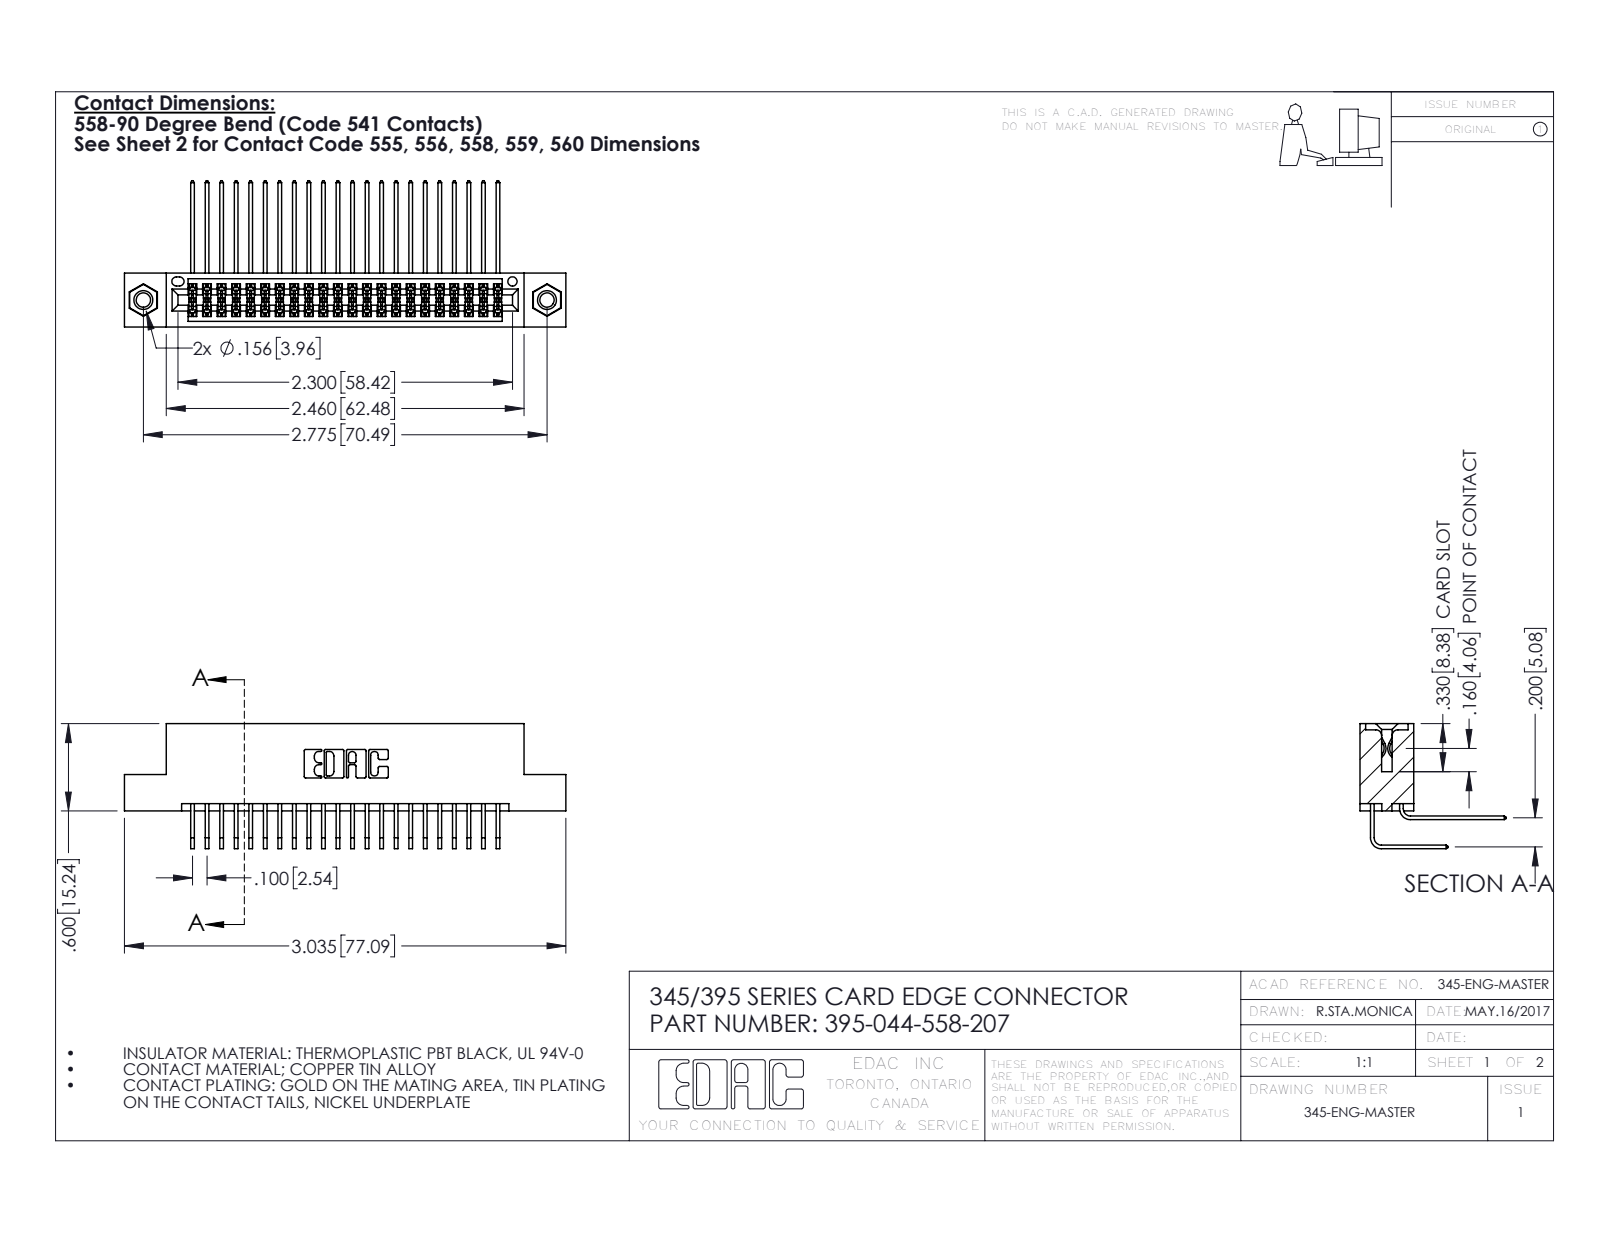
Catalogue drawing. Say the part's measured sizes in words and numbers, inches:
The part is named "345 Part_Flush Mounting Lugs - 0.156 Dia-TI; 345-250-001_345-250-005-103; 345-292-001_558 Tail - 2; 345-292-001_558 559 Tail - 1 (+1 more)". Its 3-D file was written by "SolidWorks 2016 (CONFIG_CONTROL_DESIGN)". It is 47 solids with 2474 faces: 1652 planar, 806 cylindrical and 16 other. Overall it measures 3.035 by 1.005 by 0.859 inches. Its volume is 0.46 cubic inches and its surface area 18.58 square inches. Round holes: 2 of diameter 0.098, 2 of diameter 0.125, 2 of diameter 0.156, 1 of diameter 0.064. Round bosses or shafts: 2 of diameter 0.155. Partial cylindrical surfaces (rounded edges, fillets, slot ends): 67 of radius 0.006, 22 of radius 0.01, 6 of radius 0.007, 6 of radius 0.031, 3 of radius 0.026, 2 of radius 0.014, 2 of radius 0.019, 2 of radius 0.022. The main face-to-face distances are 0.2, 0.072, 0.298, 0.37, 0.098, 0.272, 0.025, 0.225, 0.285, 0.025. The hole center spacings are 0.27, 2.541, 2.775.
